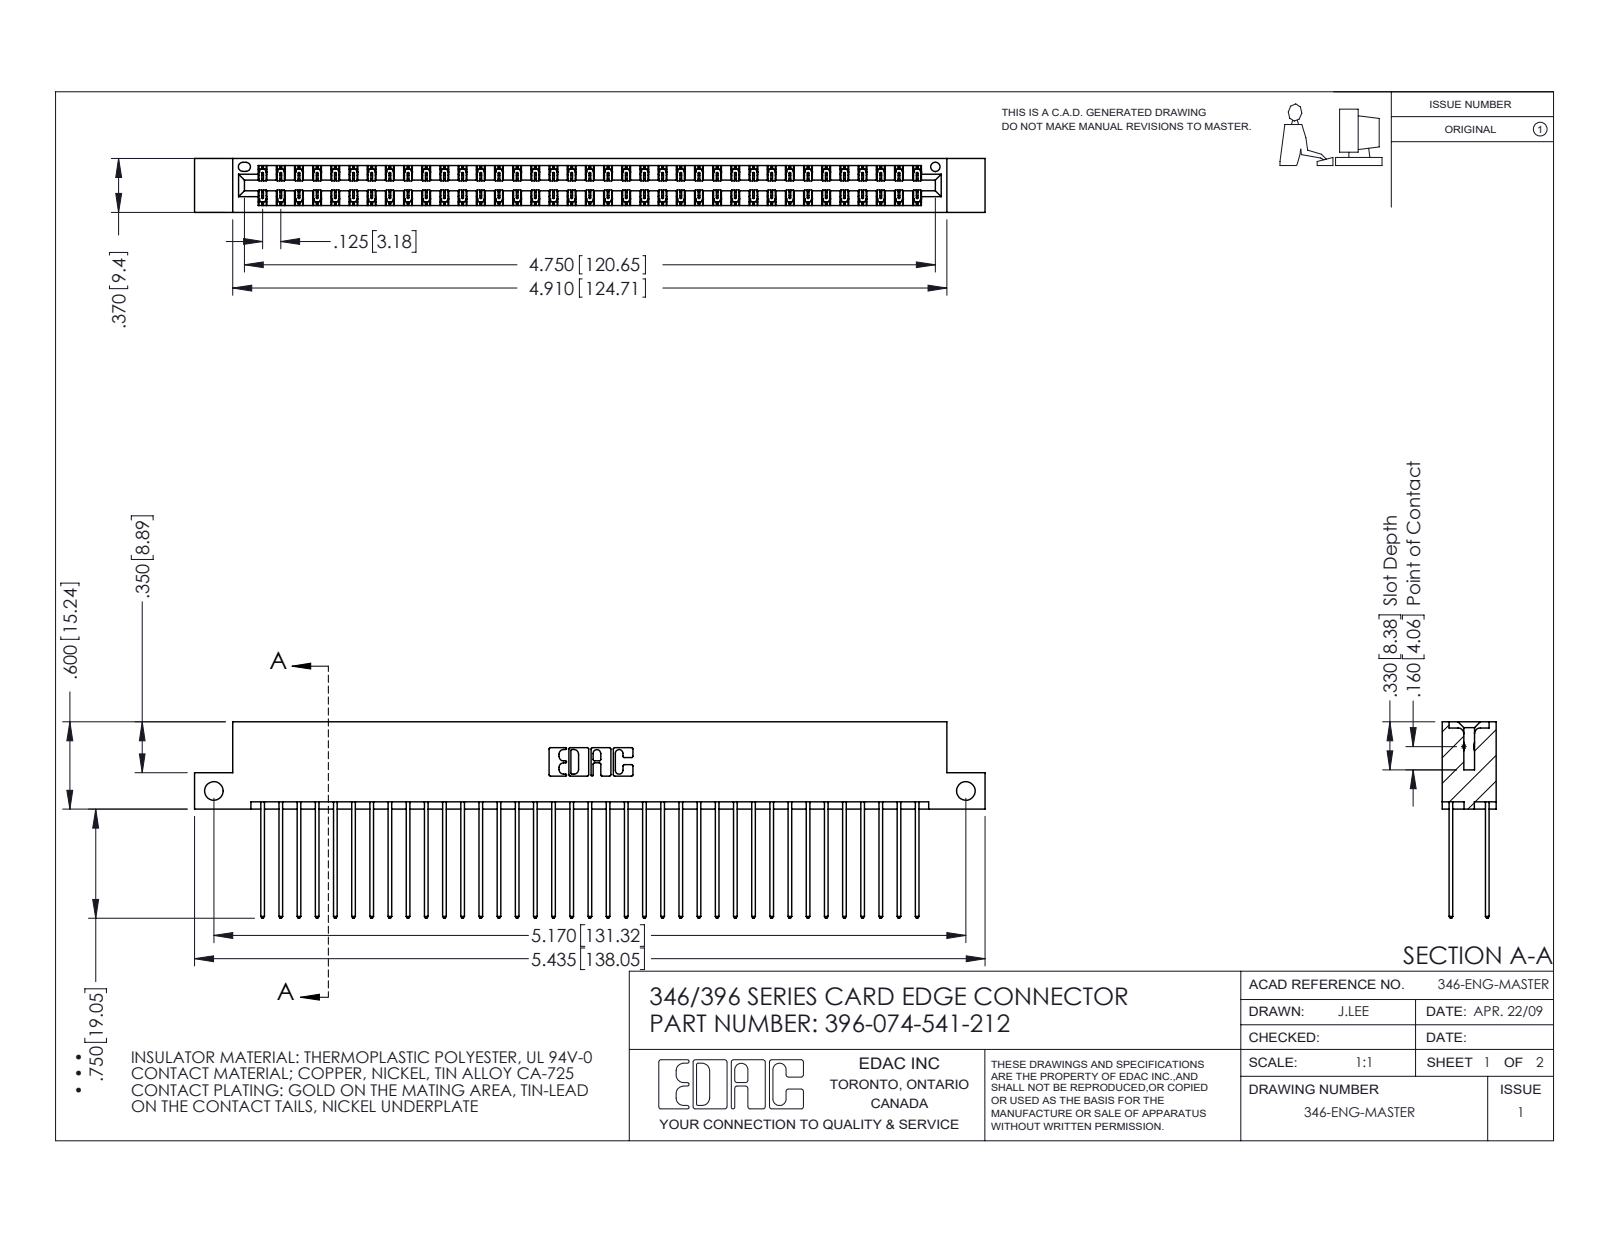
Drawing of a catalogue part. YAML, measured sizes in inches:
part_name: "346 Part_Flush Mounting Lugs - Side Mount; 396-074-541-212; 345-292-001_345-293-141"
step_written_by: "SolidWorks 2016 (CONFIG_CONTROL_DESIGN)"
units: inches
bodies: {solids: 75, faces: 3970, planar: 2666, cylindrical: 1304, other: 0}
overall_size: [5.435, 1.35, 0.37]
volume: 0.84
surface_area: 32.14
round_holes:
  - {diameter: 0.128, count: 2}
  - {diameter: 0.064, count: 1}
partial_cylinders:
  - {radius: 0.006, count: 111}
  - {radius: 0.01, count: 74}
  - {radius: 0.01, count: 22}
  - {radius: 0.007, count: 6}
  - {radius: 0.031, count: 6}
  - {radius: 0.026, count: 3}
  - {radius: 0.014, count: 2}
  - {radius: 0.022, count: 2}
face_to_face_distances: [0.048, 0.322, 0.25, 0.072, 0.298, 0.025, 0.37, 0.275, 0.225, 0.148]
hole_center_spacings: [5.17]
